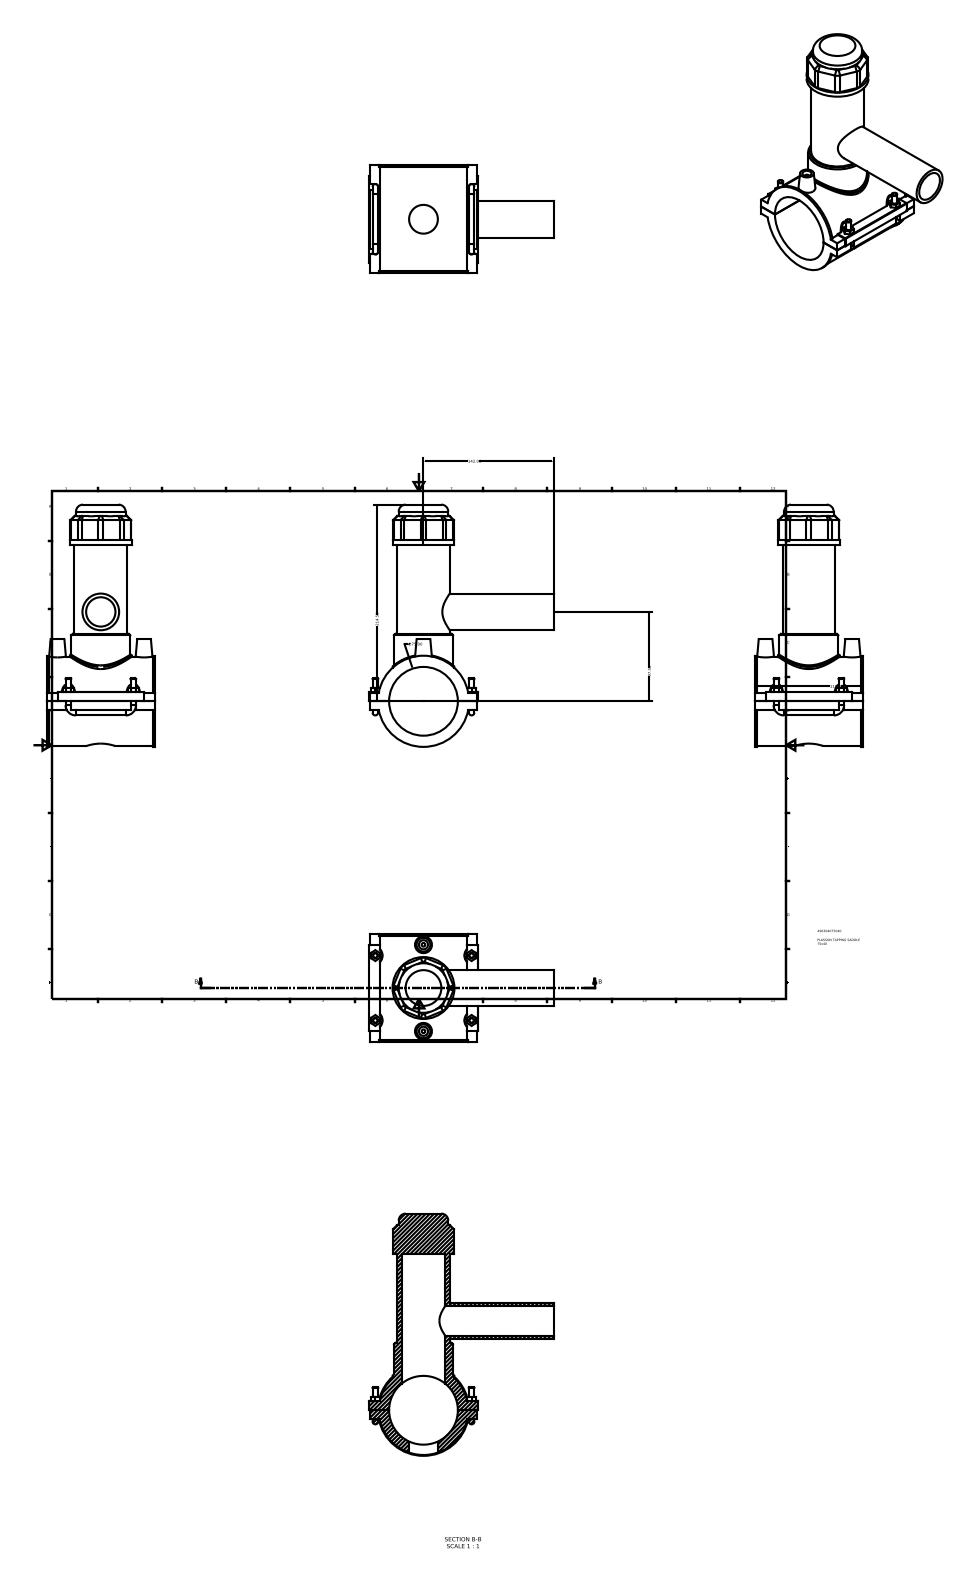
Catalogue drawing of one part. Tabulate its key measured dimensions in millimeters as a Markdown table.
| quantity | value |
| --- | --- |
| part name | 496304075040 |
| STEP written by | Autodesk Inventor 2015 (AUTOMOTIVE_DESIGN) |
| units | millimeters |
| bodies | 1 solid, 192 faces (118 planar, 49 cylindrical, 25 other) |
| overall size | 264.23 × 201.5 × 118 |
| volume | 692 327 mm³ |
| surface area | 172 327 mm² |
| round holes (diameter × count) | 10 × 2, 31.36 × 1, 32 × 1, 47.25 × 1, 75 × 1 |
| round bosses / shafts (diameter × count) | 6 × 6, 4 × 2, 99.45 × 1, 97.5 × 1, 67.5 × 1, 64.12 × 1, 57.38 × 1, 54 × 1 |
| partial cylindrical surfaces (radius × count) | 7.5 × 12, 3 × 4, 0.5 × 1, 50.7 × 1 |
| main face-to-face distances | 118, 170.3, 170.2, 9.33, 9.43, 1, 179.63, 19.76, 10.43, 10.33 |
| hole center spacings | 47.2, 94.4 |
